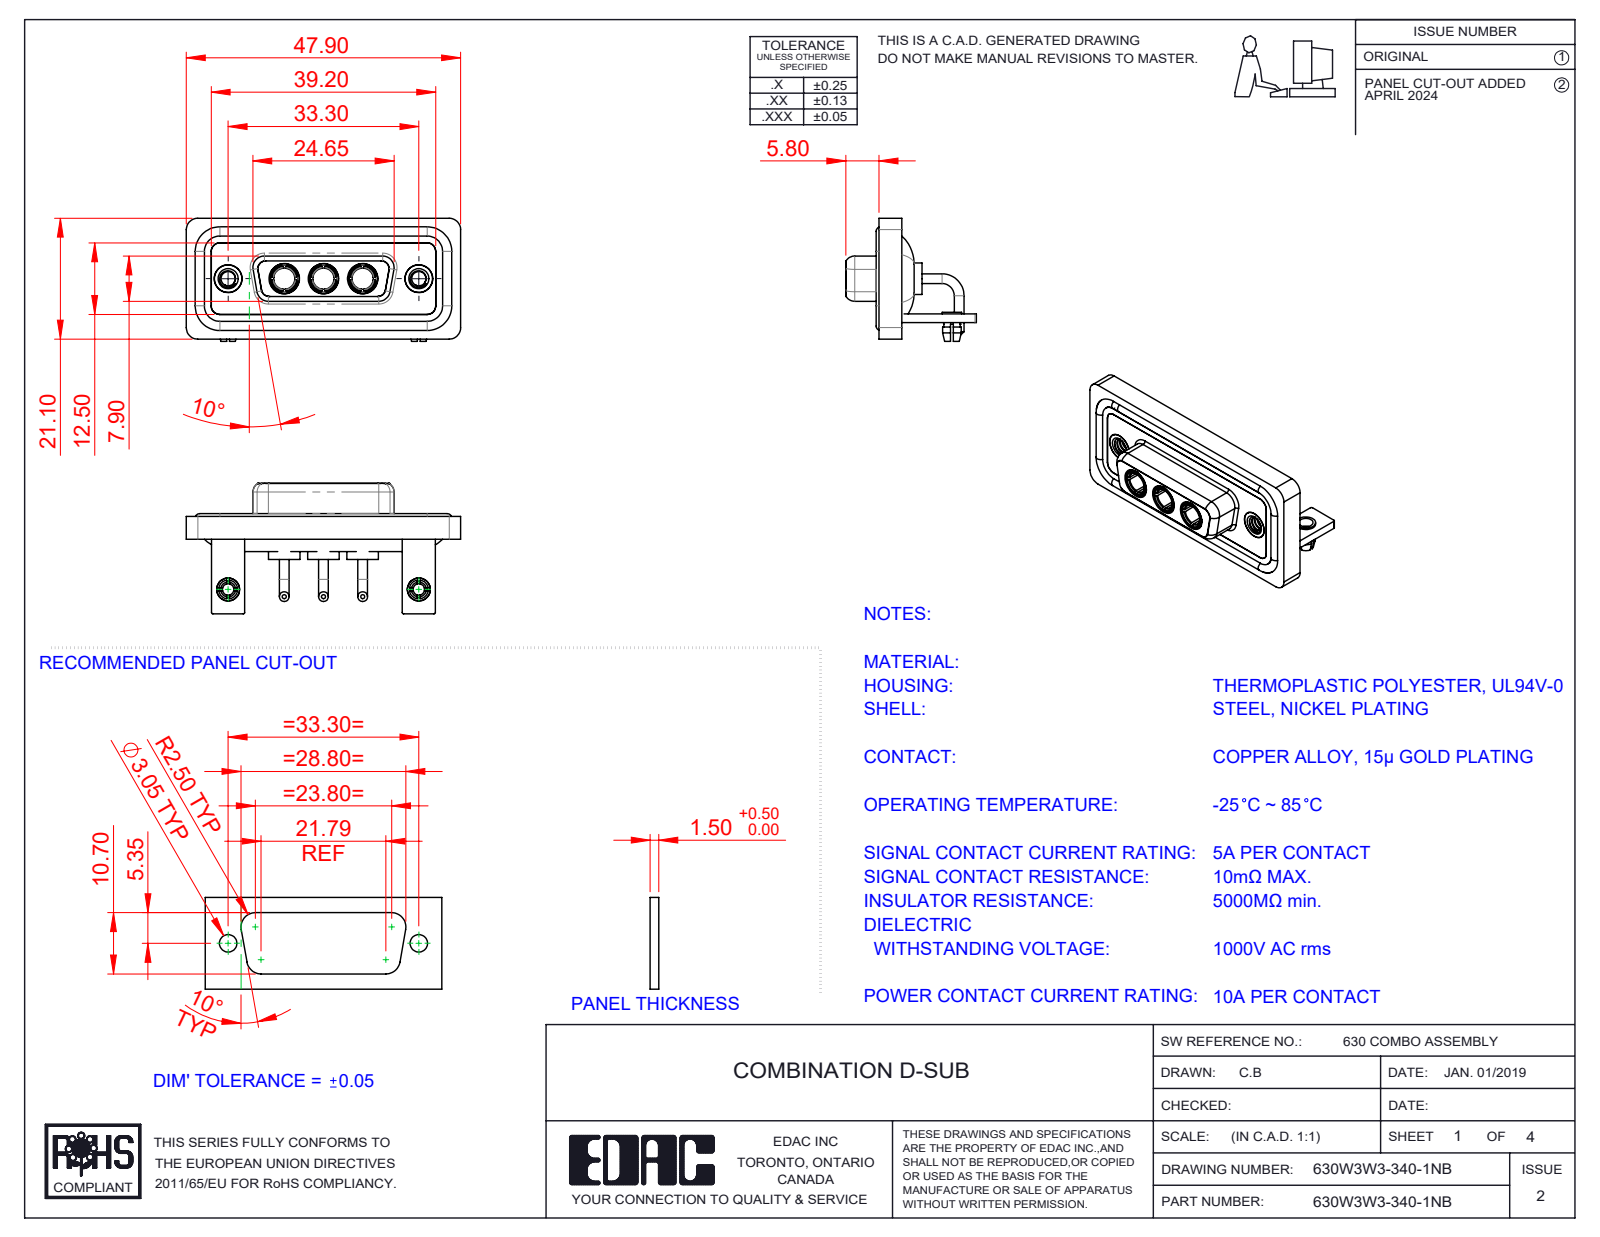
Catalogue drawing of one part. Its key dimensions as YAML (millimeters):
part_name: "630Combo Shell Front_15 Contacts; 630W3W3-340-1NB; 630Combo Waterproof Housing_15 Contacts; 630Combo Housing_3W3 (+5 more)"
step_written_by: "SolidWorks 2023 (CONFIG_CONTROL_DESIGN)"
units: millimeters
bodies: {solids: 17, faces: 754, planar: 260, cylindrical: 317, other: 177}
overall_size: [47.9, 22.8, 21.5]
volume: 6402
surface_area: 10769
round_holes:
  - {diameter: 4.85, count: 5}
  - {diameter: 2.5, count: 4}
  - {diameter: 3.7, count: 3}
  - {diameter: 5.3, count: 3}
  - {diameter: 2, count: 2}
  - {diameter: 3.2, count: 2}
  - {diameter: 4, count: 2}
  - {diameter: 4.05, count: 2}
  - {diameter: 5, count: 2}
round_bosses_or_shafts:
  - {diameter: 1.7, count: 6}
  - {diameter: 1.6, count: 4}
  - {diameter: 5.5, count: 3}
  - {diameter: 5.2, count: 3}
  - {diameter: 4.96, count: 3}
  - {diameter: 4.75, count: 3}
  - {diameter: 3.75, count: 3}
  - {diameter: 4.95, count: 2}
partial_cylinders:
  - {radius: 2, count: 21}
  - {radius: 1.5, count: 18}
  - {radius: 0.25, count: 16}
  - {radius: 1.35, count: 12}
  - {radius: 1.6, count: 8}
  - {radius: 0.5, count: 5}
  - {radius: 0.6, count: 4}
  - {radius: 0.65, count: 4}
face_to_face_distances: [0.4, 2.9, 1.5, 1.8, 3.7, 1.1, 4.1, 1.6, 2.5, 1.4]
hole_center_spacings: [6.85, 9.8, 16.65, 23.5, 33.3, 13.7]
